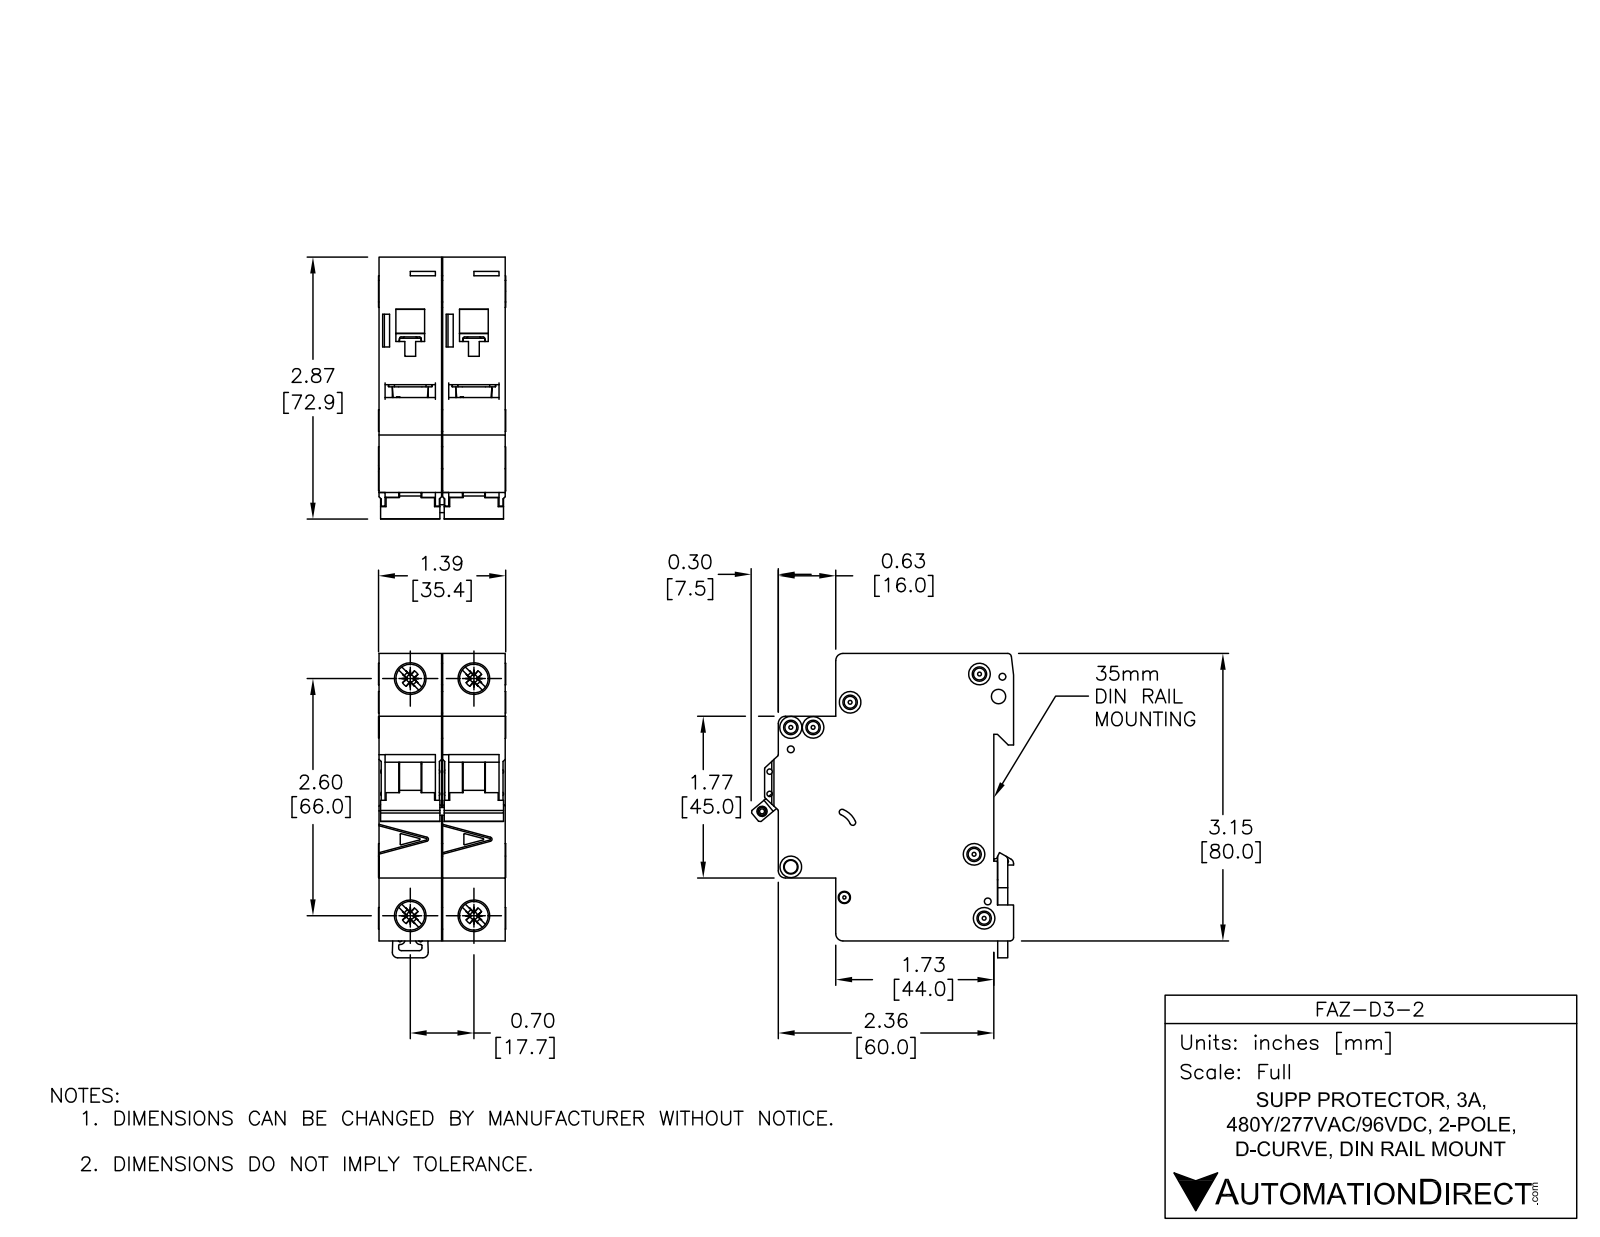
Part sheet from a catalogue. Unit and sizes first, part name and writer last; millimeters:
Units: millimetres
Overall size (bounding box): 84.78 × 73.04 × 35.4
Round holes (diameter × count): ⌀3.6 ×6, ⌀1.9 ×3, ⌀1.09 ×2, ⌀1.5 ×2, ⌀4 ×2, ⌀7.15 ×2, ⌀8.2 ×2, ⌀2.15 ×1, ⌀2.2 ×1, ⌀2.55 ×1, ⌀3.3 ×1, ⌀3.4 ×1
Round bosses / shafts (diameter × count): ⌀6 ×4, ⌀8.2 ×2, ⌀2.5 ×2
Partial cylindrical surfaces — rounded edges, fillets, slot ends (radius × count): R0.25 ×49, R0.5 ×19, R2 ×10, R0.2 ×8, R1 ×8, R0.8 ×2, R1.8 ×2, R3 ×2
Main face-to-face distances: 17.7, 17.5, 35.2, 79.48, 5.5, 49.5, 44, 65.5, 60, 16
Hole centre spacings: 6.2, 13.64, 17.7, 66, 68.33, 4.81, 5.19, 5.61
Volume: 149 808 mm³ · Surface area: 38 799 mm²
Bodies: 8 solids, 1104 faces (466 planar, 396 cylindrical, 242 other)
Part name (STEP PRODUCT): FAZ-D3-2
STEP written by: SolidWorks 2014 (AUTOMOTIVE_DESIGN)
